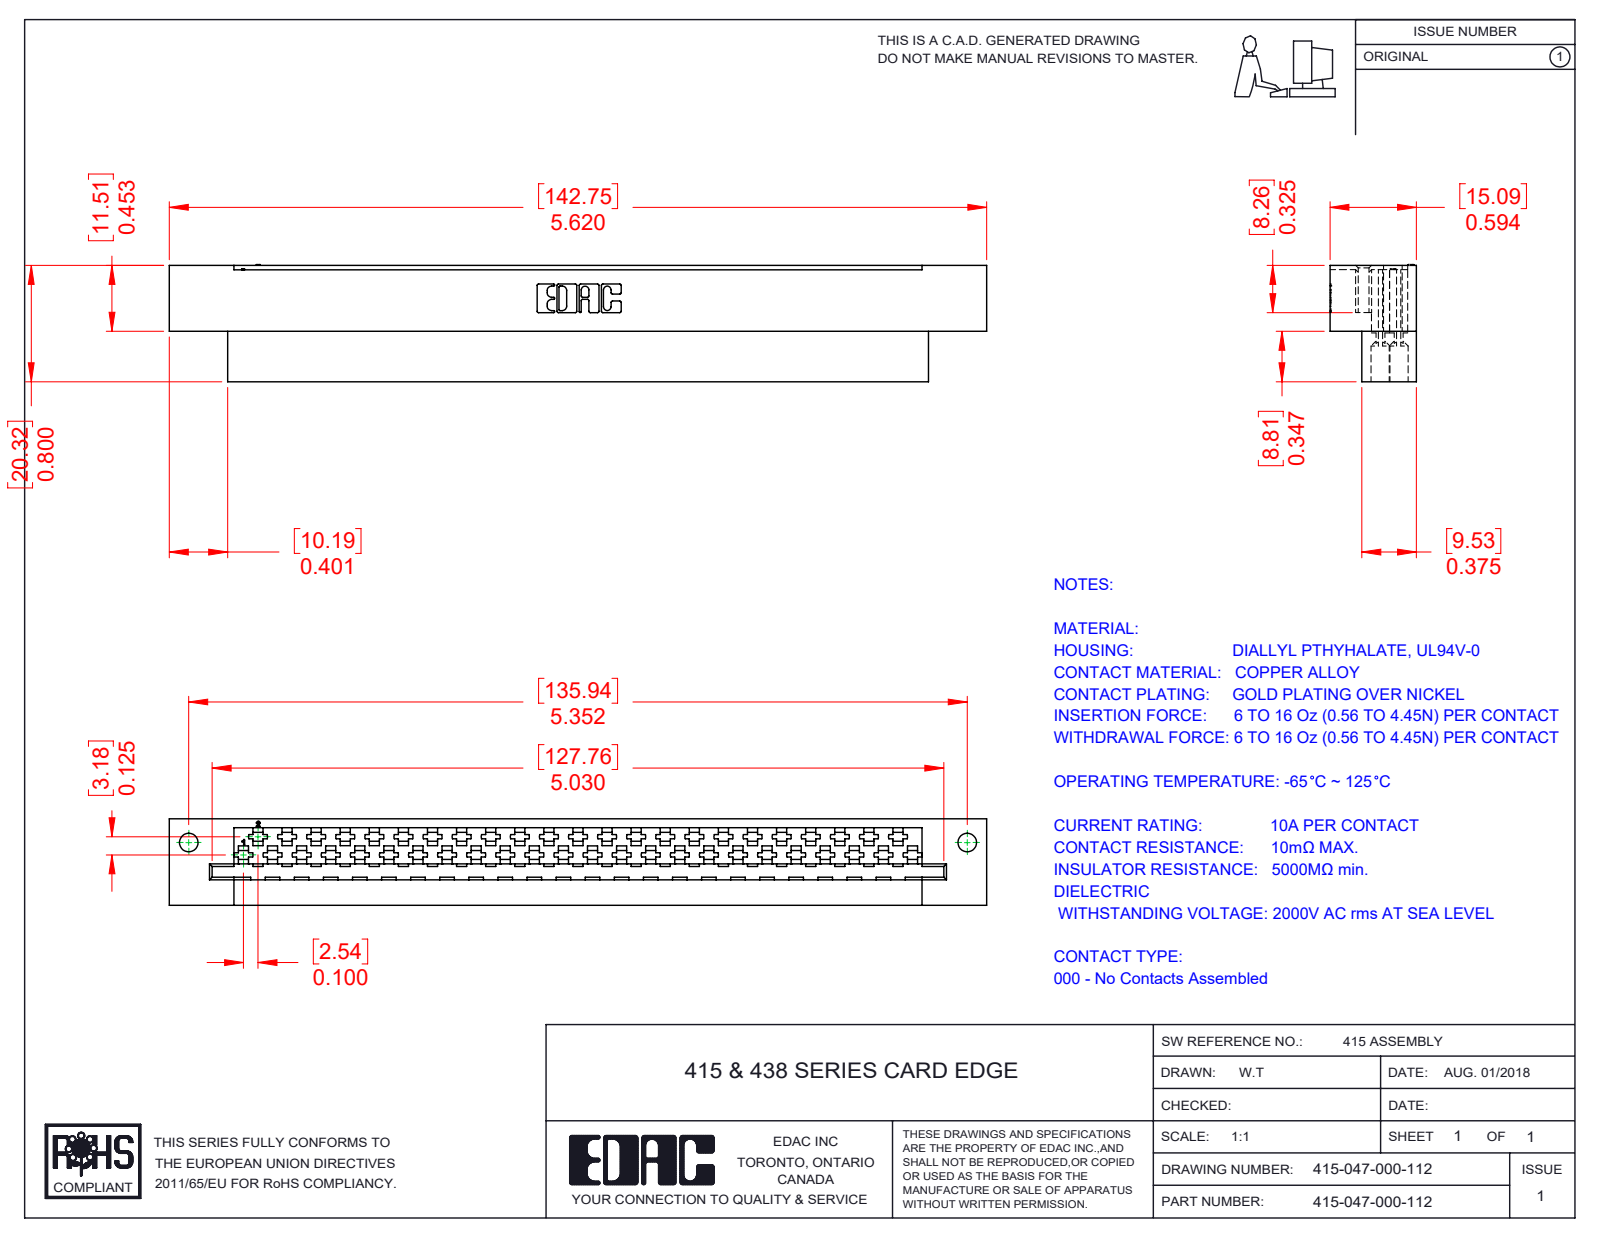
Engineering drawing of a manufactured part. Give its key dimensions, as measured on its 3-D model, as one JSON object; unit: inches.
{"part_name": "415-210-001_415-210-047-112; 415-047-000-112", "step_written_by": "SolidWorks 2016 (CONFIG_CONTROL_DESIGN)", "units": "inches", "bodies": {"solids": 1, "faces": 1366, "planar": 1065, "cylindrical": 138, "other": 163}, "overall_size": [5.62, 0.805, 0.594], "volume_in3": 1.519, "surface_area_in2": 34.56, "round_holes": [[0.13, 47], [0.128, 2]], "partial_cylinders_radius": [[0.01, 22], [0.007, 6], [0.031, 6], [0.026, 3]], "face_to_face_distances": [0.594, 0.076, 0.125, 0.375, 0.219, 0.048, 0.423, 0.078, 0.124, 0.347], "hole_center_spacings": [0.2, 0.4, 0.6, 0.8, 1, 1.2, 1.4, 1.6]}
